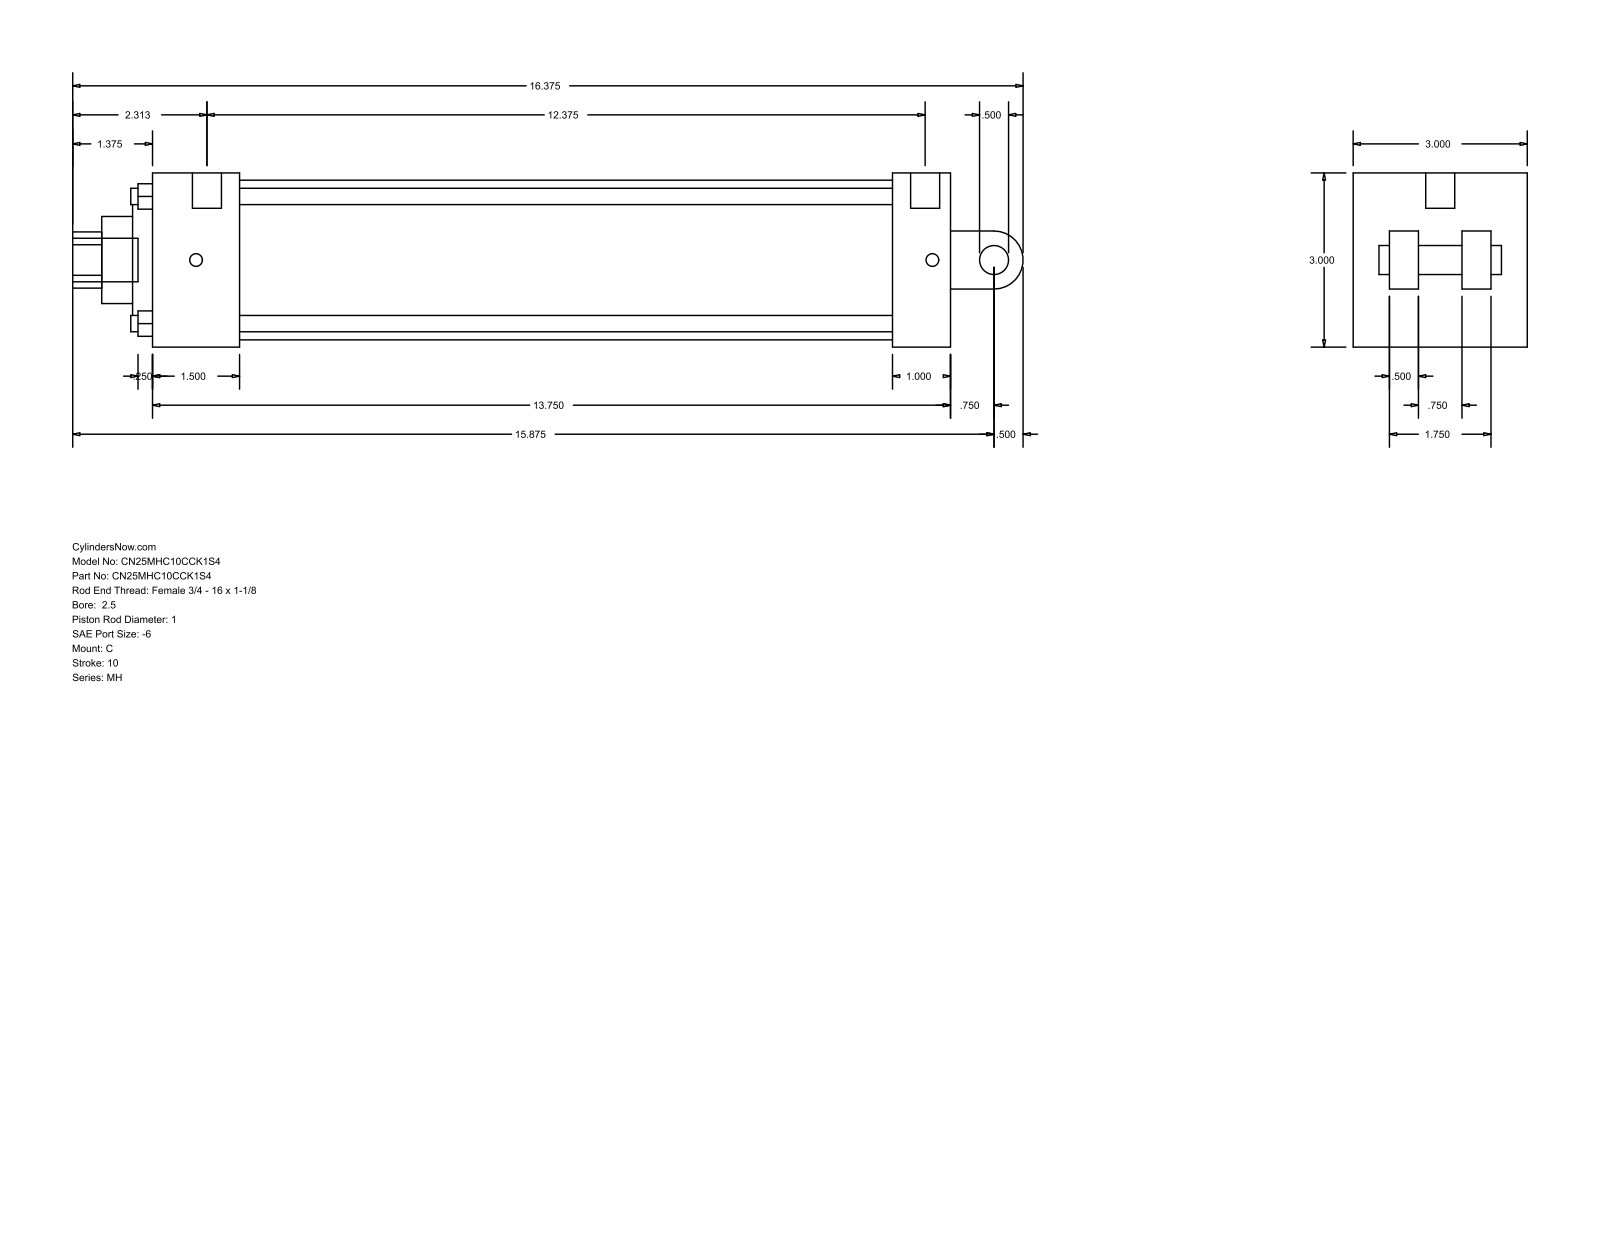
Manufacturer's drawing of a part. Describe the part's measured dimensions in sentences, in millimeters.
The part is named "MH_C__0250_1". Its 3-D file was written by "GSSL Pune (CONFIG_CONTROL_DESIGN)". It is 0 solids with 101 faces: 71 planar, 30 cylindrical and 0 other. Overall it measures 415.93 by 76.2 by 76.2 millimeters. Round holes: 4 of diameter 7.14, 2 of diameter 5.56, 1 of diameter 12.7, 1 of diameter 25.4, 1 of diameter 38.1, 1 of diameter 60.33, 1 of diameter 69.85. Round bosses or shafts: 2 of diameter 12.7, 2 of diameter 5.56, 1 of diameter 19.05. Partial cylindrical surfaces (rounded edges, fillets, slot ends): 1 of radius 12.29, 1 of radius 12.7. The main face-to-face distances are 76.2, 349.26, 15.87, 60.33, 323.85, 25.41, 38.11, 285.74, 311.15, 12.7. The hole center spacings are 39.33, 55.62, 78.66, 3.18.
